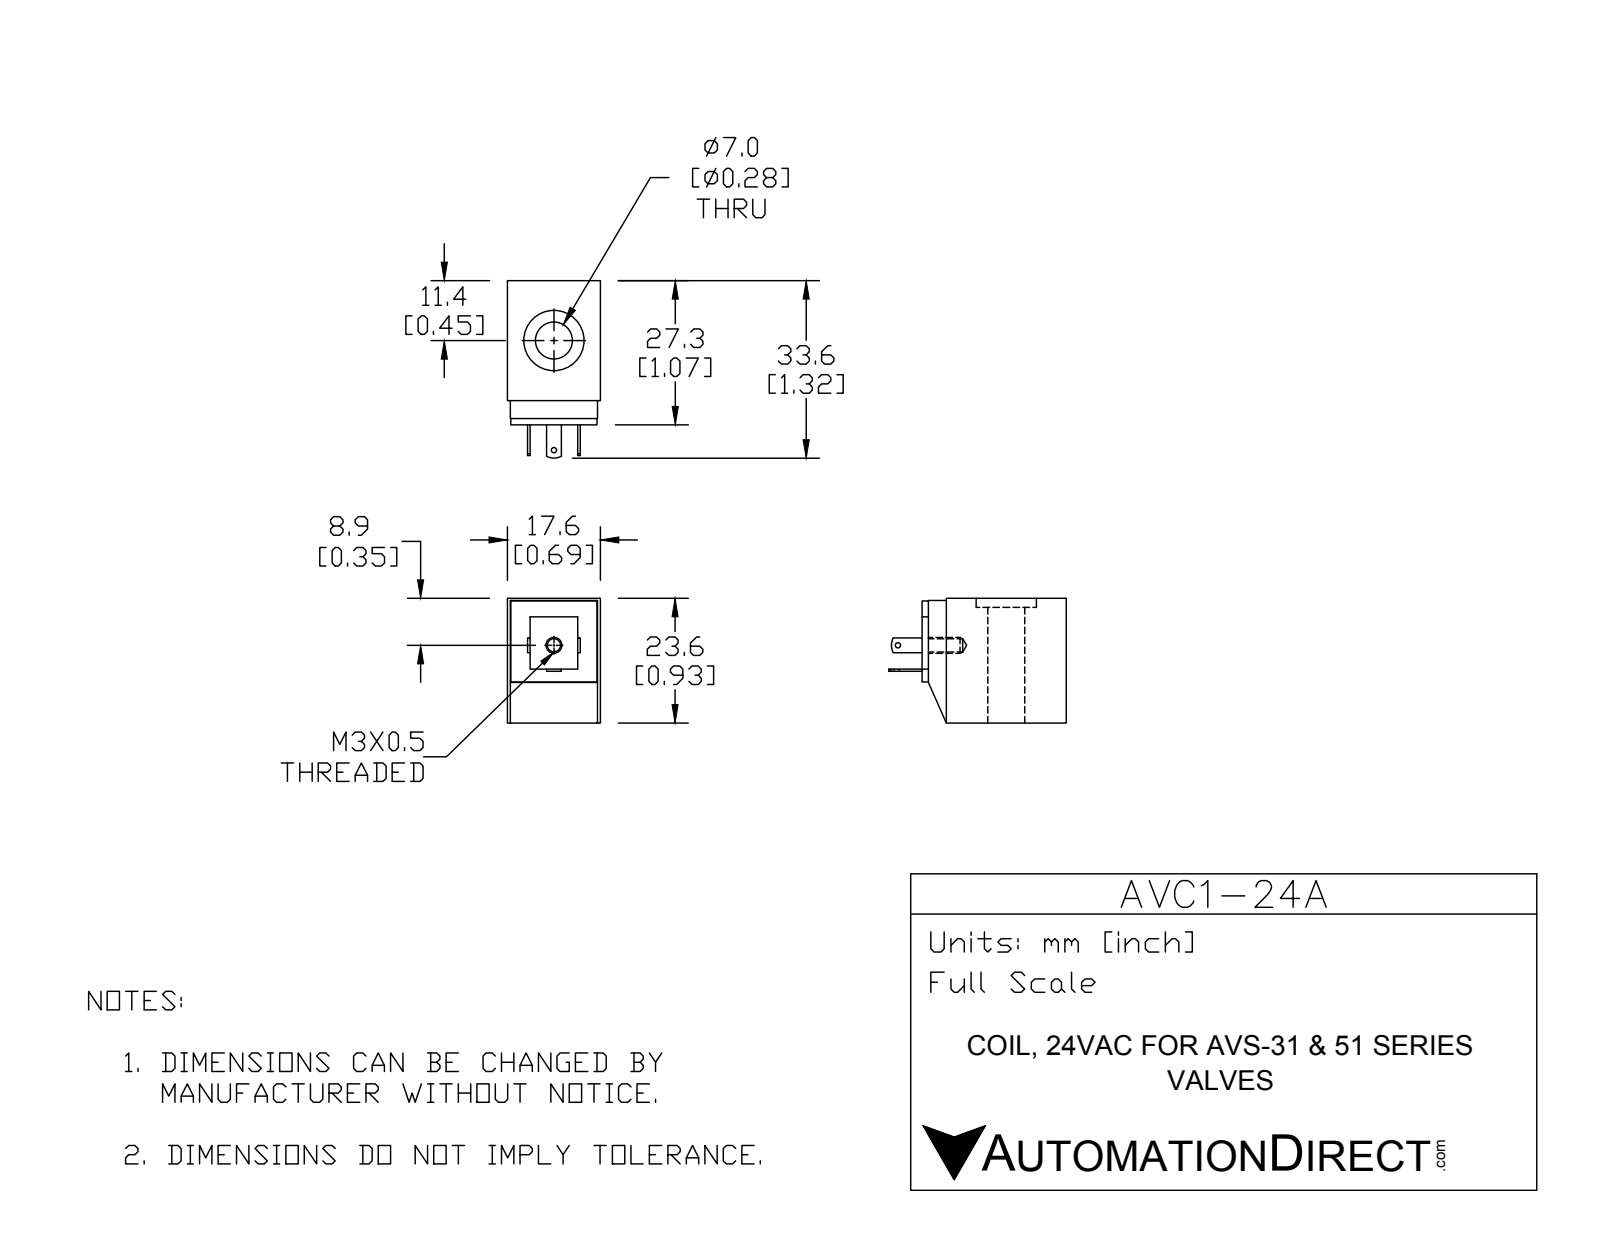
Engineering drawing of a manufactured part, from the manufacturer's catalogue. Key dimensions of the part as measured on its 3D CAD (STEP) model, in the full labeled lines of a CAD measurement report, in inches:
Part name (STEP PRODUCT): AVC1-24A
STEP written by: SolidWorks 2016 (AUTOMOTIVE_DESIGN)
Units: inches
Bodies: 1 solid, 69 faces (31 planar, 32 cylindrical, 6 other)
Overall size (bounding box): 1.323 × 0.929 × 0.693
Volume: 0.591 in³ · Surface area: 5.65 in²
Round holes (diameter × count): ⌀0.039 ×2, ⌀0.098 ×1, ⌀0.276 ×1, ⌀0.449 ×1
Partial cylindrical surfaces — rounded edges, fillets, slot ends (radius × count): R0.004 ×16, R0.118 ×2
Main face-to-face distances: 0.693, 0.929, 1.075, 0.022, 0.671, 0.047, 1.028, 0.524, 0.016, 0.65
Hole centre spacings: 0.817
